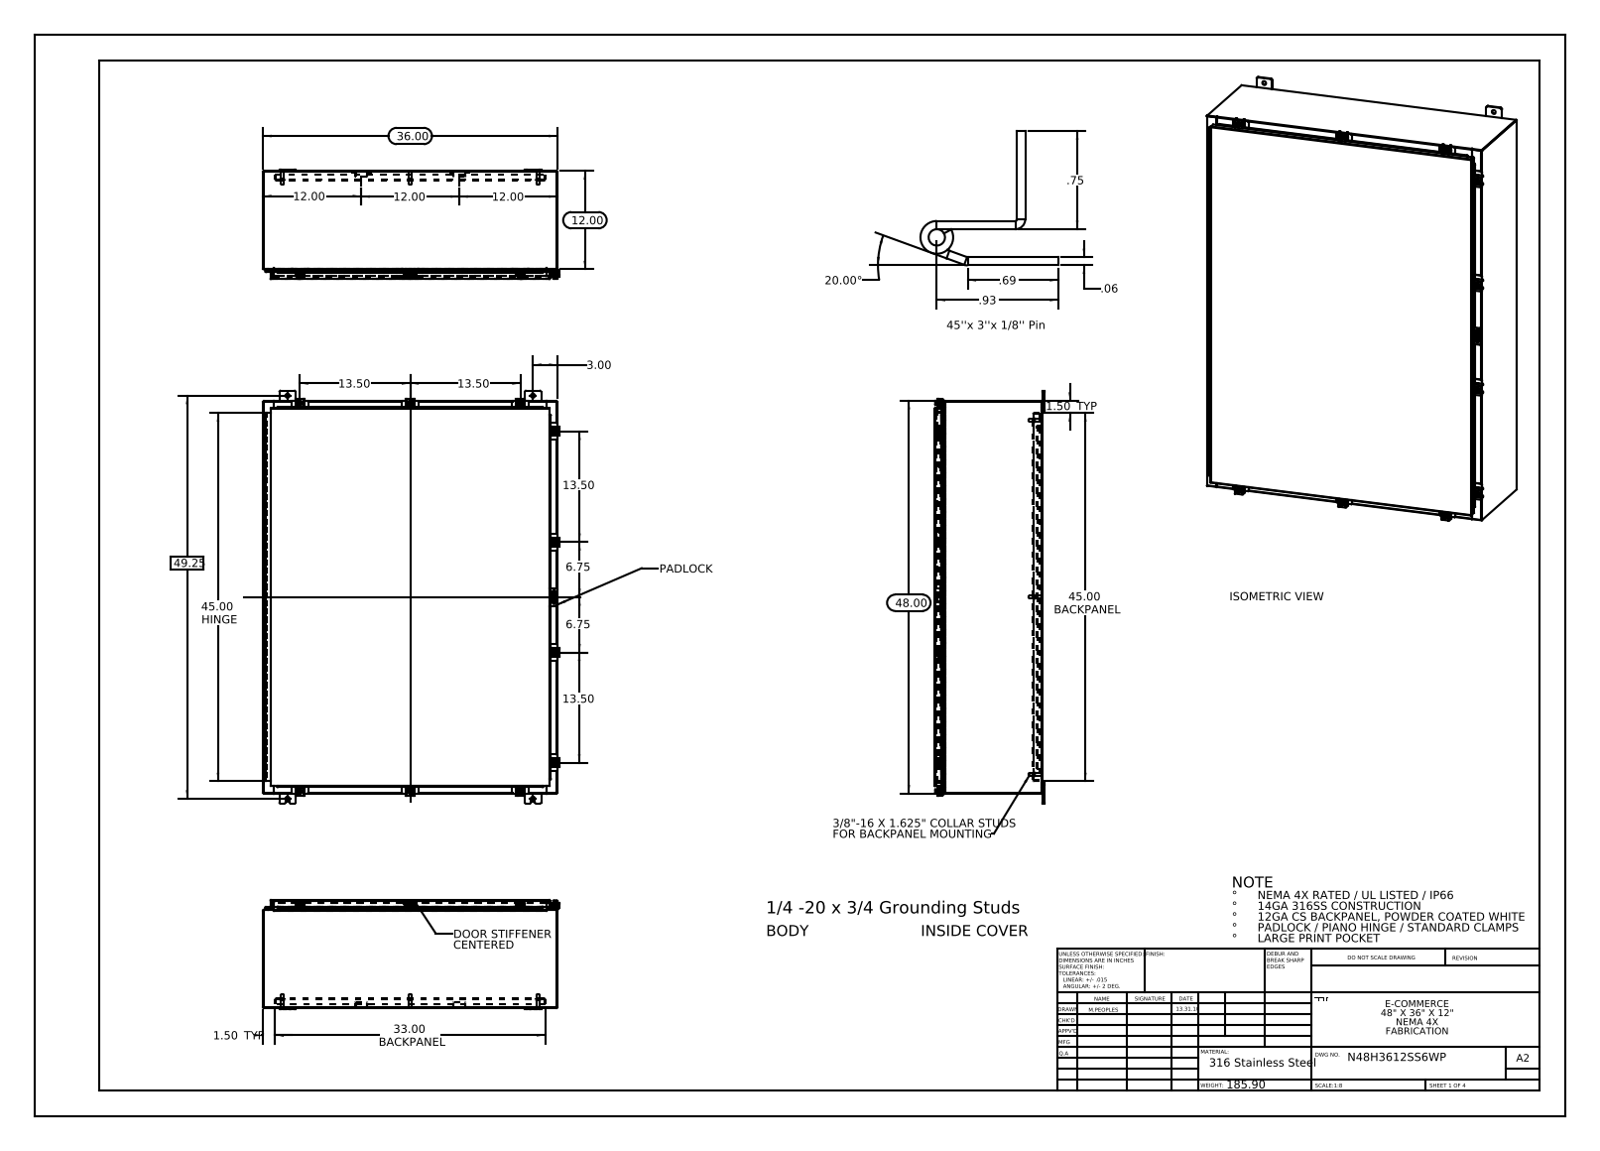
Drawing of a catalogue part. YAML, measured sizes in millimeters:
part_name: "N48H3612SS6WP Door Stiffener; N48H3612SS6WP Mounting Feet; N48H3612SS6WP Enclosure Stiffener; N48H3612SS6WP Mounting Studs (+8 more)"
step_written_by: "SolidWorks 2013 (CONFIG_CONTROL_DESIGN)"
units: millimeters
bodies: {solids: 74, faces: 2999, planar: 1562, cylindrical: 1269, other: 168}
overall_size: [1282.7, 919.8, 340.1]
volume: 10660000
surface_area: 10490000
round_holes:
  - {diameter: 12.7, count: 12}
  - {diameter: 5.4, count: 10}
  - {diameter: 6.6, count: 10}
  - {diameter: 6.4, count: 6}
  - {diameter: 3.2, count: 2}
  - {diameter: 3.2, count: 1}
round_bosses_or_shafts:
  - {diameter: 6.4, count: 11}
  - {diameter: 12.7, count: 10}
  - {diameter: 10.1, count: 10}
  - {diameter: 15.9, count: 8}
  - {diameter: 9.5, count: 8}
  - {diameter: 8.4, count: 8}
partial_cylinders:
  - {radius: 1.5, count: 46}
  - {radius: 0.3, count: 39}
  - {radius: 2.2, count: 33}
  - {radius: 4.8, count: 24}
  - {radius: 3, count: 20}
  - {radius: 3.6, count: 20}
  - {radius: 1.3, count: 15}
  - {radius: 2, count: 14}
face_to_face_distances: [1.9, 333.4, 331.5, 2.6, 335.3, 25.4, 308, 27.3, 306.1, 29.9]
hole_center_spacings: [342.9, 347, 508, 511.1, 549.3, 605, 685.8, 965.3]
